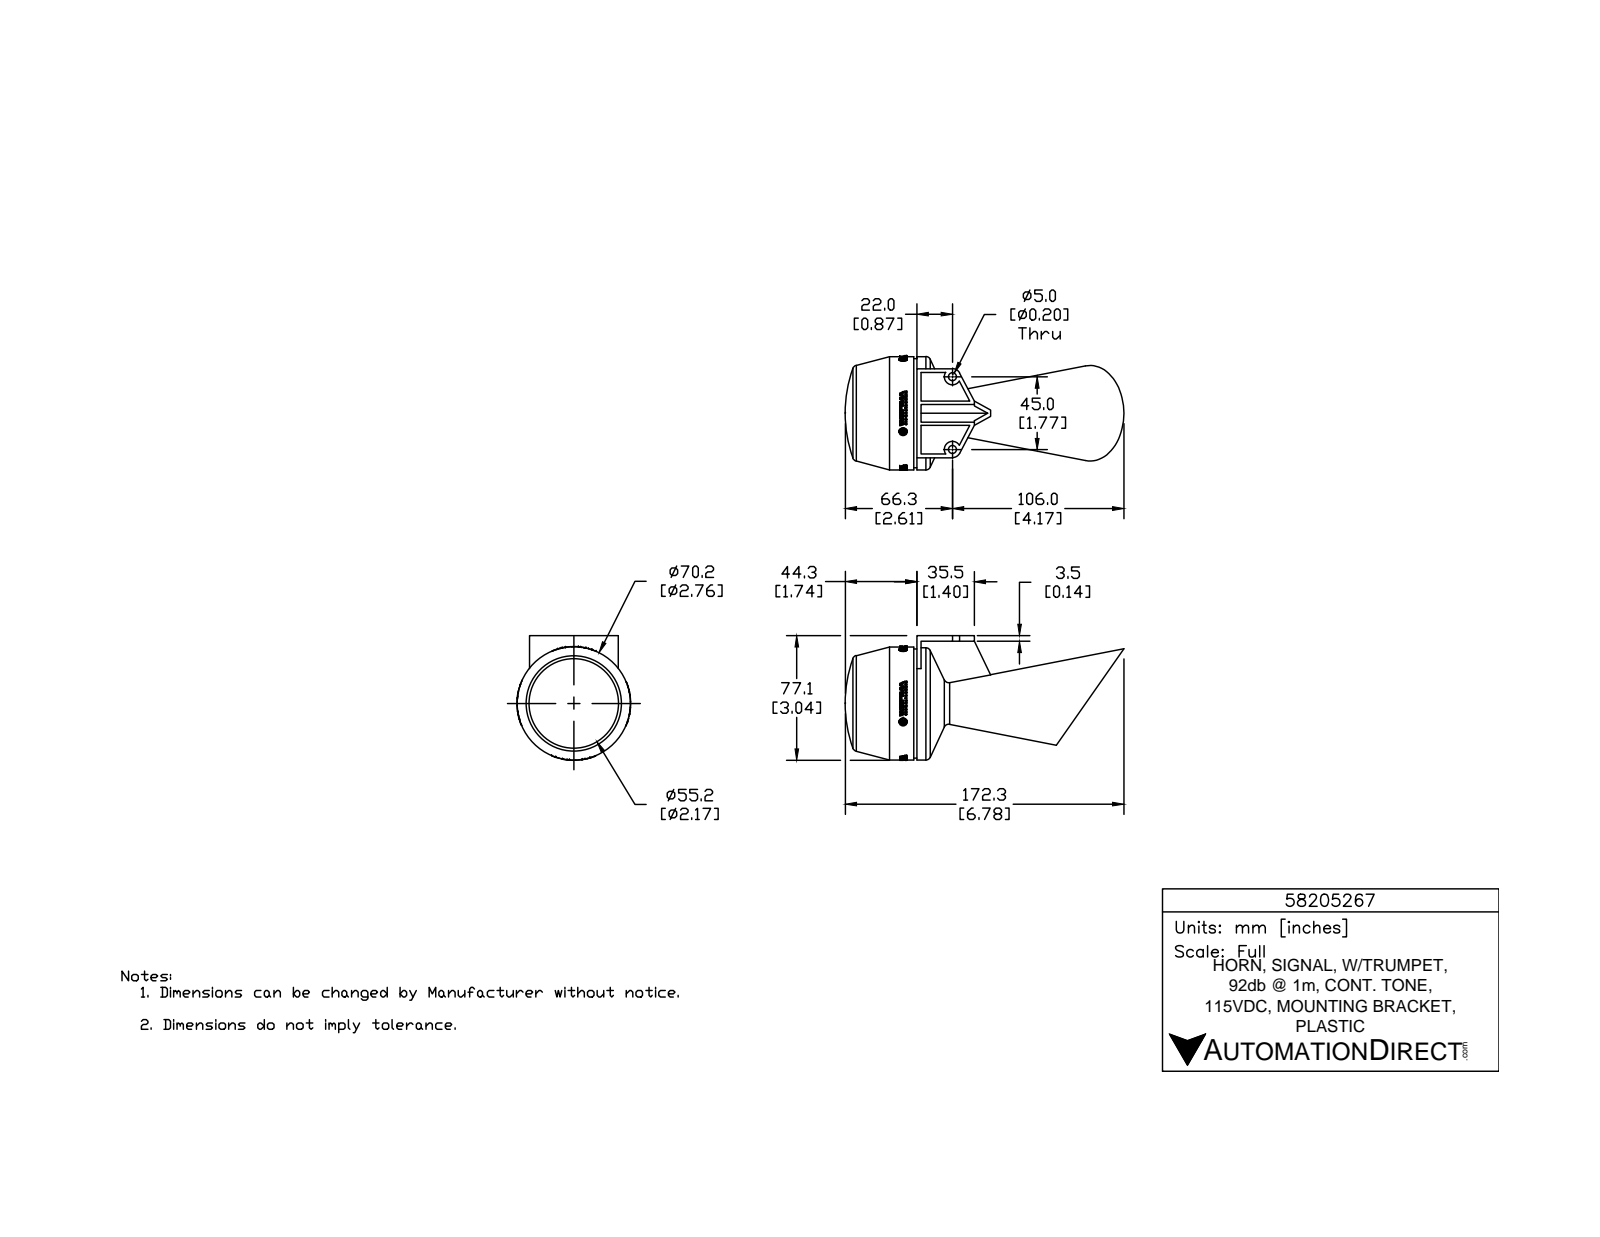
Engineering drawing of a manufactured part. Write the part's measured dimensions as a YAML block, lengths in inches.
part_name: "58205267"
step_written_by: "SolidWorks 2017 (AUTOMOTIVE_DESIGN)"
units: inches
bodies: {solids: 1, faces: 1036, planar: 590, cylindrical: 119, other: 327}
overall_size: [6.783, 3.035, 2.764]
volume: 20.08
surface_area: 60.58
round_holes:
  - {diameter: 0.197, count: 2}
round_bosses_or_shafts:
  - {diameter: 2.756, count: 1}
  - {diameter: 2.657, count: 1}
partial_cylinders:
  - {radius: 0.197, count: 2}
  - {radius: 1.382, count: 1}
face_to_face_distances: [0.098, 0.112, 0.112, 0.039, 0.138, 0.177, 0.079, 2.165, 0.787, 1.378]
hole_center_spacings: [1.772]
